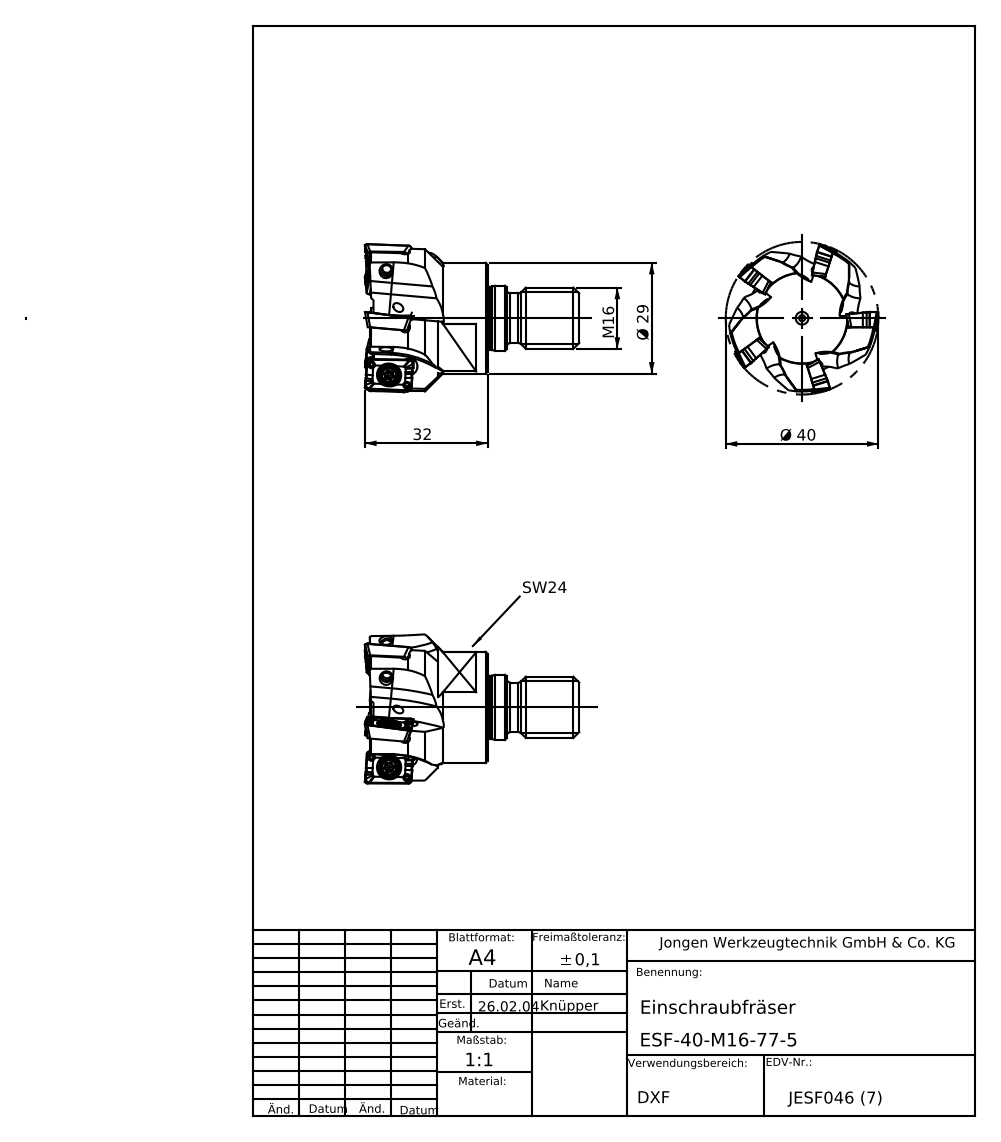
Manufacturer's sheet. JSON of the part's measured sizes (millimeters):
{"part_name": "ESF-40-M16-77-5", "step_written_by": "SolidWorks 2013 (AUTOMOTIVE_DESIGN)", "units": "millimeters", "bodies": {"solids": 1, "faces": 106, "planar": 37, "cylindrical": 32, "other": 37}, "overall_size": [55.99, 40.08, 40.08], "volume_mm3": 31614, "surface_area_mm2": 8842, "round_holes": [[2.1, 5], [1.6, 1], [4, 1]], "round_bosses_or_shafts": [[29, 1], [17, 1], [16.6, 1], [16, 1], [13, 1]], "partial_cylinders_radius": [[2, 10], [23.54, 5], [19.2, 1]], "face_to_face_distances": [29.9, 24, 53.9, 16.9, 13, 37, 26.9, 10, 3, 27]}
